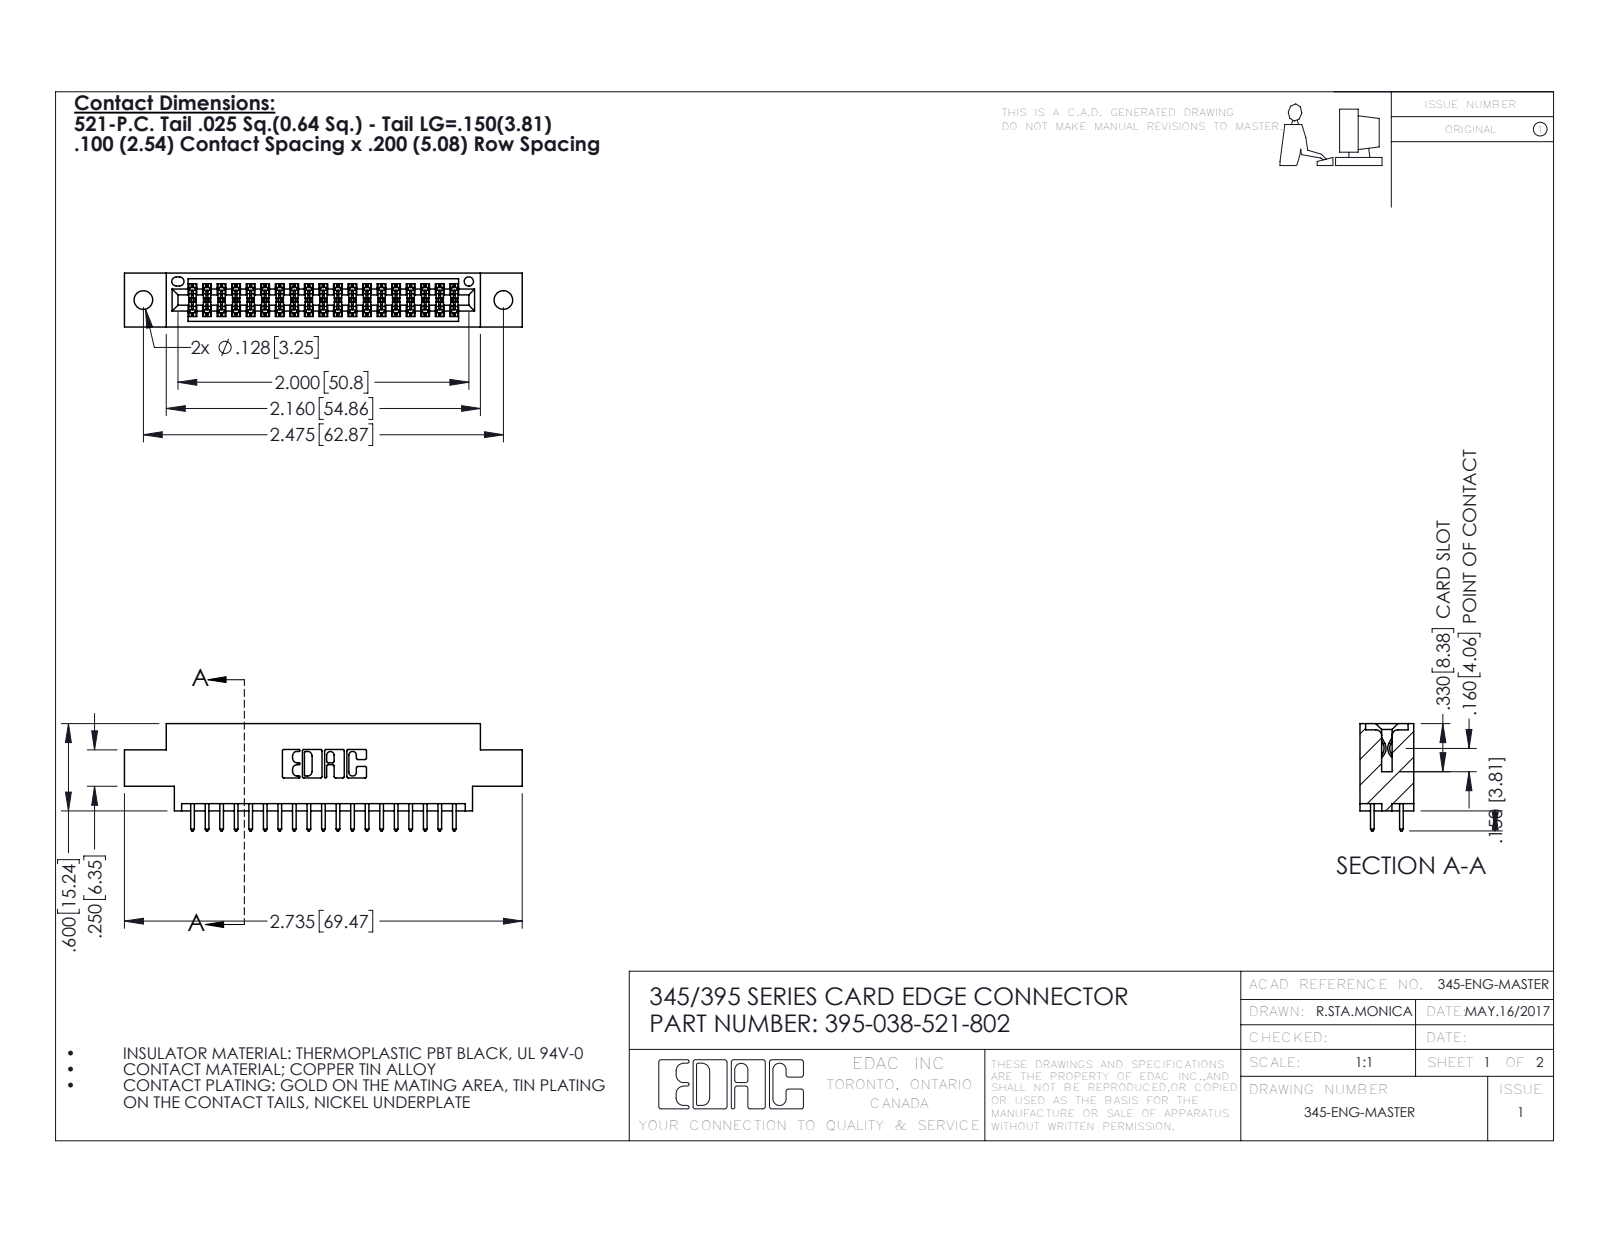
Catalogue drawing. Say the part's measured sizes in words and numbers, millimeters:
The part is named "345-292-001_345-293-121; 395-038-521-802; 345 Part_0.170 Offset - 0.128 Dia". Its 3-D file was written by "SolidWorks 2016 (CONFIG_CONTROL_DESIGN)". It is 39 solids with 2030 faces: 1338 planar, 692 cylindrical and 0 other. Overall it measures 69.5 by 18.7 by 9.4 millimeters. Its volume is 6 370 cubic millimeters and its surface area 8 742 square millimeters. Round holes: 2 of diameter 3.3, 1 of diameter 1.6. Partial cylindrical surfaces (rounded edges, fillets, slot ends): 57 of radius 0.2, 38 of radius 0.3, 22 of radius 0.3, 6 of radius 0.2, 6 of radius 0.8, 3 of radius 0.7, 2 of radius 0.4, 2 of radius 0.5. The main face-to-face distances are 7.6, 1.8, 9.4, 5.1, 2.5, 6.9, 0.6, 5.7, 4.4, 2.5. The hole center spacings are 6.9, 56.9, 62.9.
